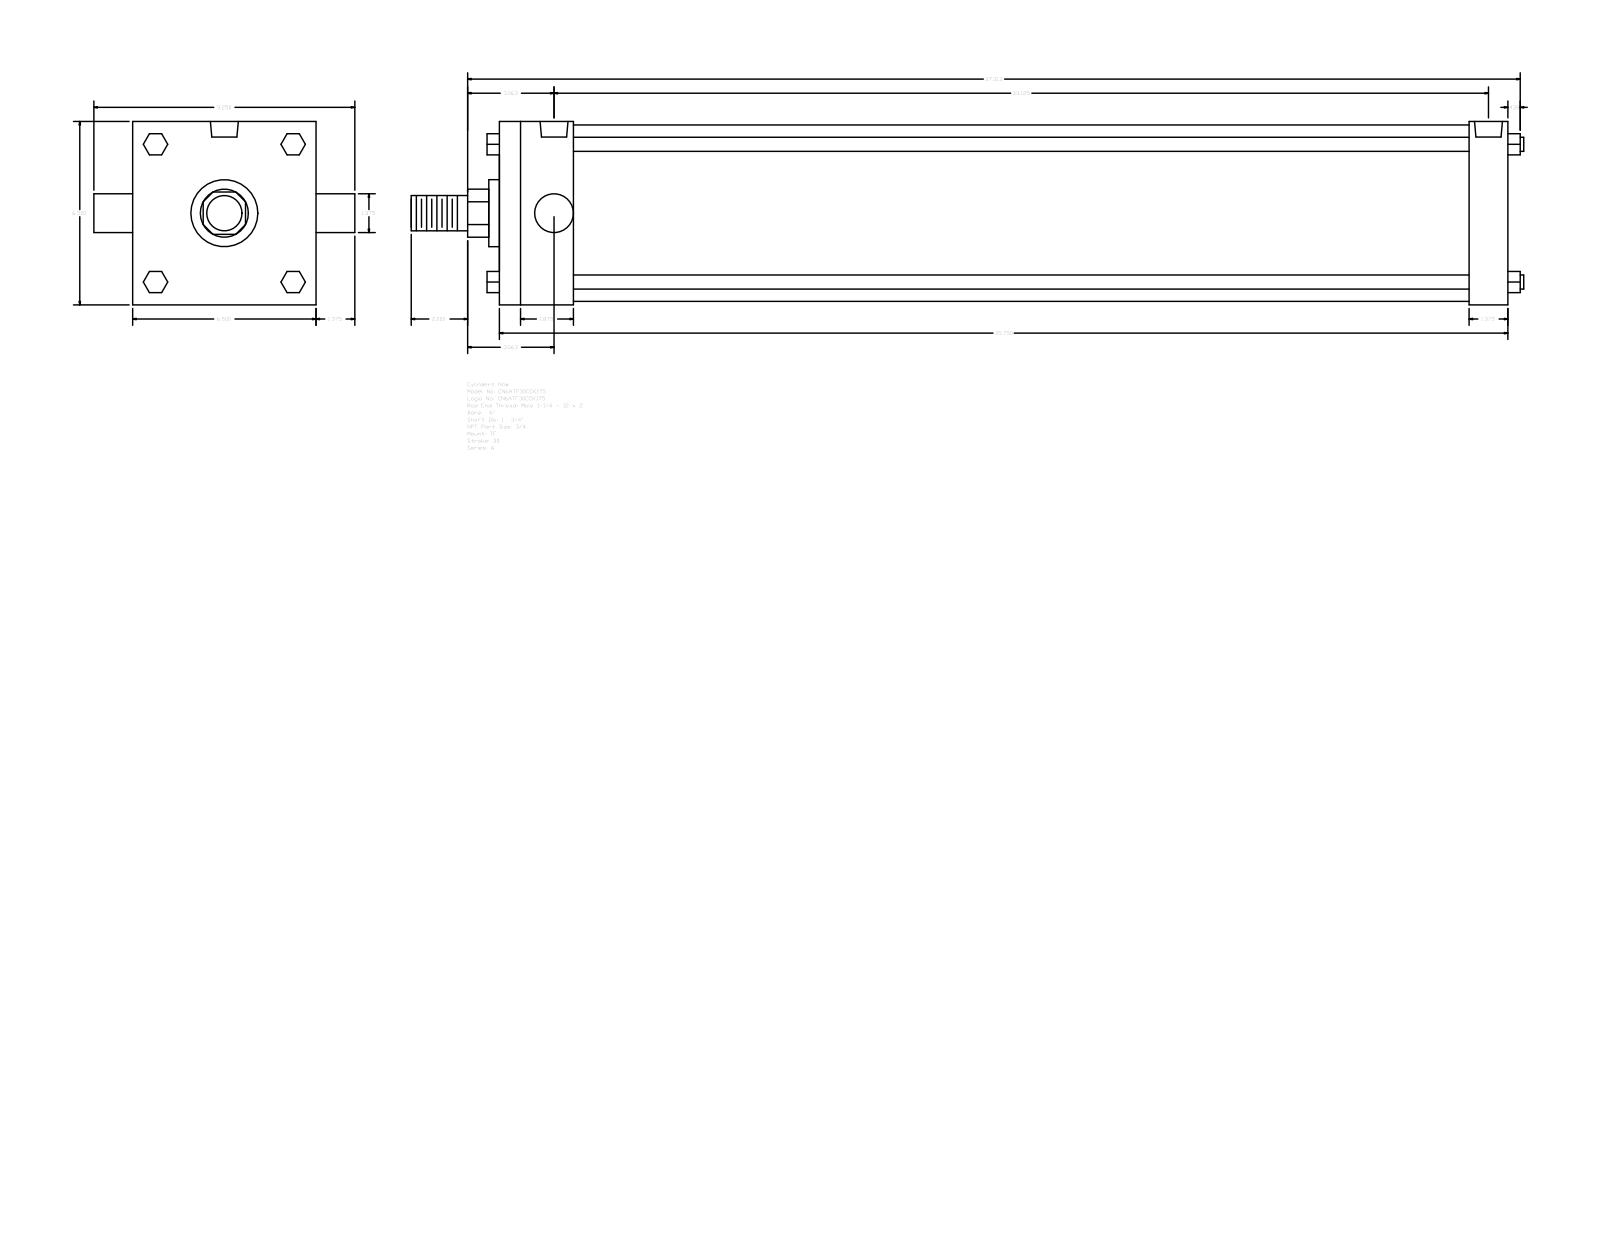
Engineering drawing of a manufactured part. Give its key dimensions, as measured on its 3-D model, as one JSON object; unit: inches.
{"part_name": "A_TF__0600_1.75", "step_written_by": "GSSL Pune (CONFIG_CONTROL_DESIGN)", "units": "inches", "bodies": {"solids": 0, "faces": 120, "planar": 92, "cylindrical": 28, "other": 0}, "overall_size": [39.437, 9.25, 6.5], "round_holes": [[0.594, 3], [0.989, 2]], "round_bosses_or_shafts": [[0.5, 4], [6.25, 1], [2.375, 1], [1.75, 1], [1.375, 1], [1.25, 1]], "partial_cylinders_radius": [[0.852, 1]], "face_to_face_distances": [6.5, 35.75, 1.375, 2.625, 33.125, 34.375, 31.75, 0.75, 2.44, 4.226], "hole_center_spacings": [0.219, 32.906, 32.687, 33.125]}
